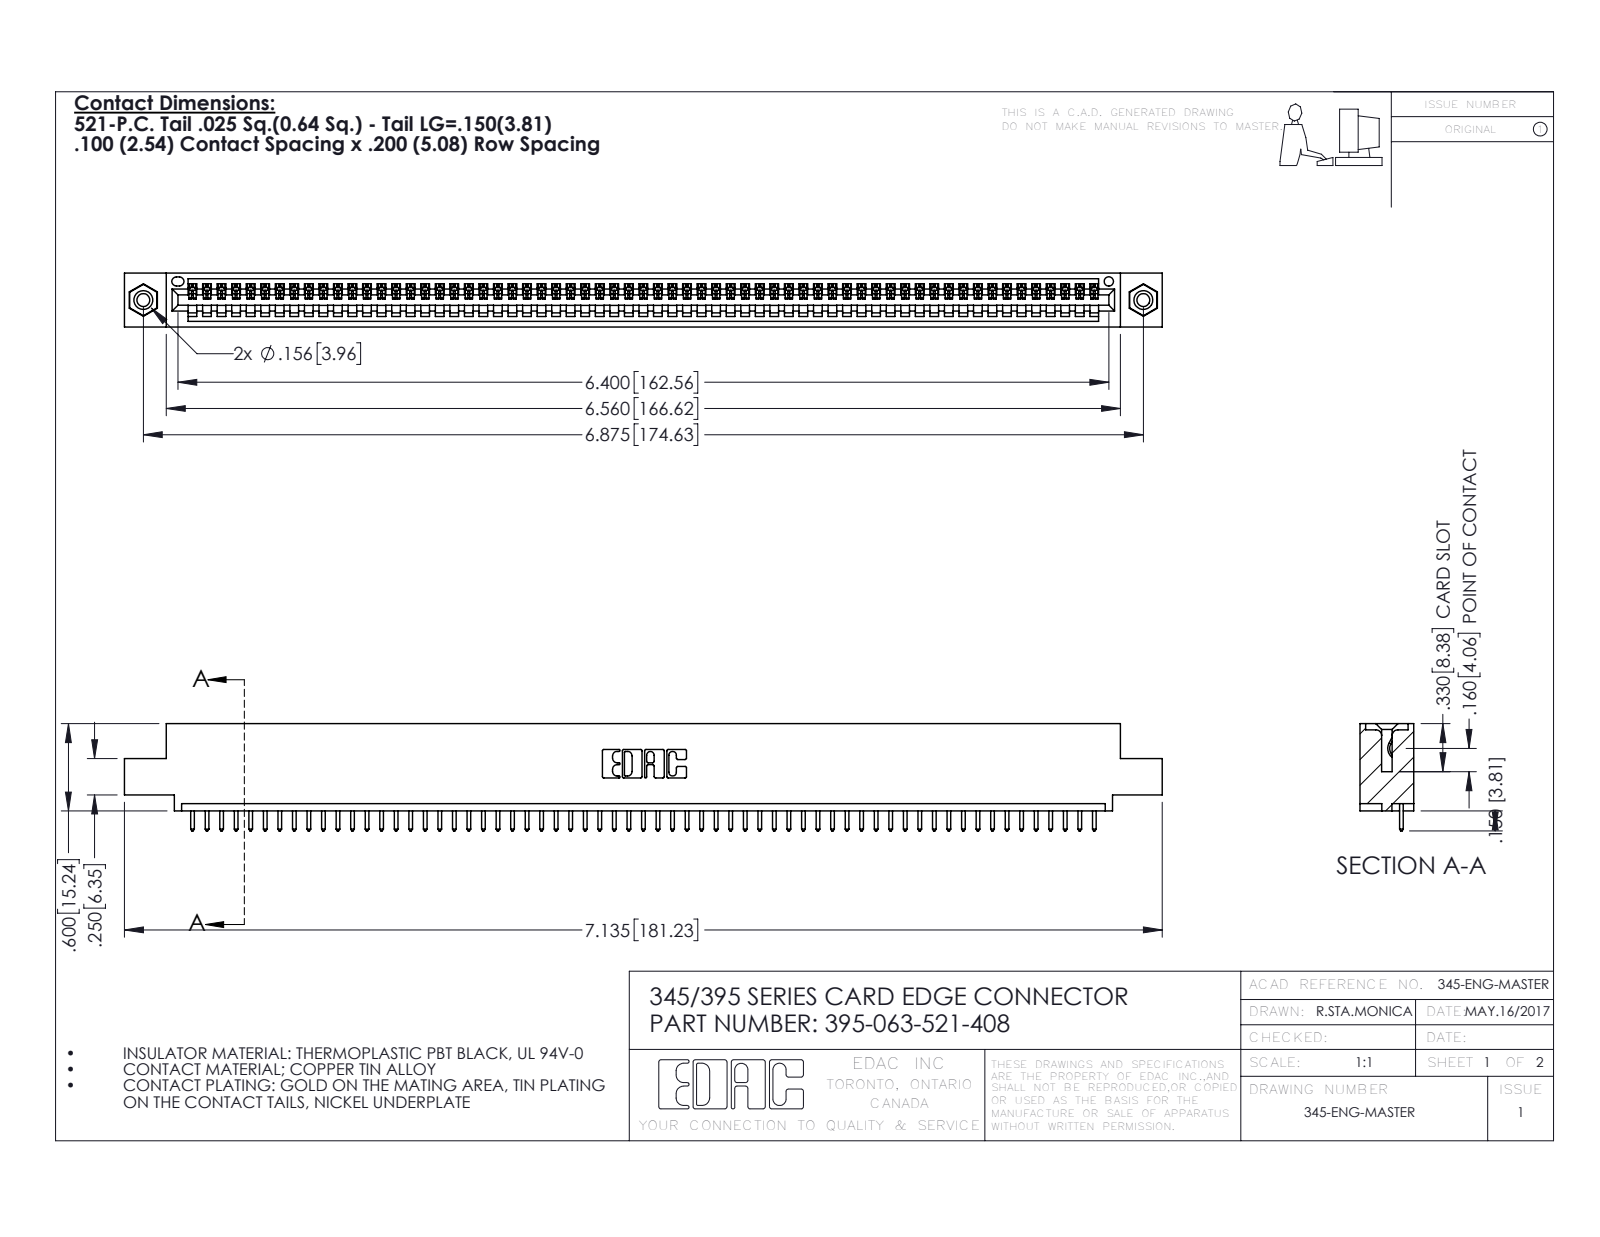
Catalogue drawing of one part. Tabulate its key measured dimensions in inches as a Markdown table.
| quantity | value |
| --- | --- |
| part name | 345 Part_0.110 Offset - 0.156 Dia-TI; 345-250-001_345-250-003-102; 345-292-001_345-293-121; 395-063-521-408 |
| STEP written by | SolidWorks 2016 (CONFIG_CONTROL_DESIGN) |
| units | inches |
| bodies | 66 solids, 3844 faces (2636 planar, 1192 cylindrical, 16 other) |
| overall size | 7.135 × 0.737 × 0.37 |
| volume | 1.045 in³ |
| surface area | 34.79 in² |
| round holes (diameter × count) | 0.089 × 2, 0.125 × 2, 0.156 × 2, 0.064 × 1 |
| round bosses / shafts (diameter × count) | 0.155 × 2 |
| partial cylindrical surfaces (radius × count) | 0.006 × 126, 0.01 × 126, 0.01 × 22, 0.007 × 6, 0.031 × 6, 0.026 × 3, 0.031 × 2, 0.04 × 2 |
| main face-to-face distances | 0.072, 0.298, 0.37, 0.2, 0.098, 0.272, 0.025, 0.225, 0.149, 0.072 |
| hole center spacings | 0.27, 6.639, 6.875 |
